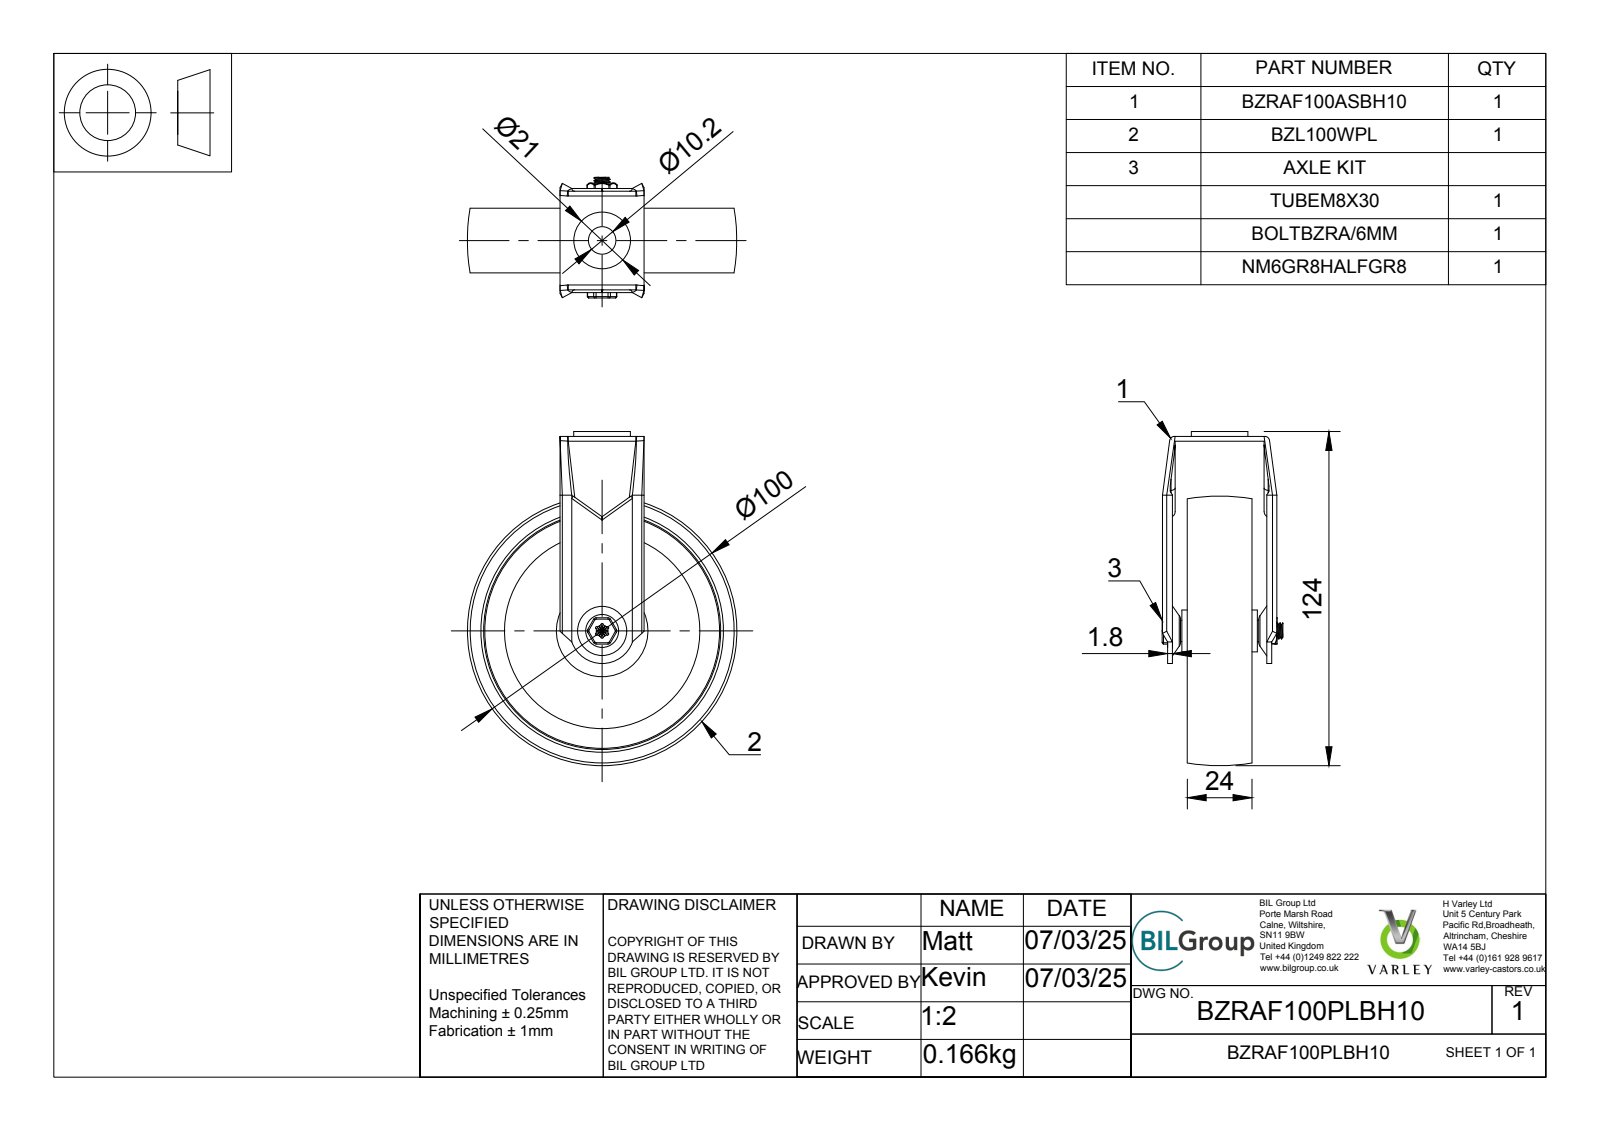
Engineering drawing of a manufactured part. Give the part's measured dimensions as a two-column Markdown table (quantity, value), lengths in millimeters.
| quantity | value |
| --- | --- |
| part name | BZRAF100PLBH10 v3; BZRAF100ASBH10 v1; ZINC PLATED PRESSED STEEL FORKS; BZL100WPL v1 (+7 more) |
| STEP written by | Autodesk Translation Framework v13.20.0.188 (AP242_MANAGED_MODEL_BASED_3D_ENGINEERING_MIM_LF) |
| units | millimeters |
| bodies | 5 solids, 277 faces (74 planar, 95 cylindrical, 108 other) |
| overall size | 124 × 100 × 44.75 |
| volume | 74 465 mm³ |
| surface area | 45 094 mm² |
| round holes (diameter × count) | 6 × 1, 6.2 × 1, 6.3 × 1, 8.2 × 1, 10.2 × 1 |
| round bosses / shafts (diameter × count) | 21 × 1, 15.5 × 1, 8 × 1, 7.95 × 1, 5.88 × 1, 4.74 × 1 |
| partial cylindrical surfaces (radius × count) | 1 × 26, 0.5 × 12, 1.5 × 8, 0.4 × 6, 0.99 × 4, 1.8 × 2, 2.12 × 1, 11.91 × 1 |
| main face-to-face distances | 1.8, 3, 10.5, 13.5, 35.8, 17.8, 1, 7.3, 16, 5.5 |
